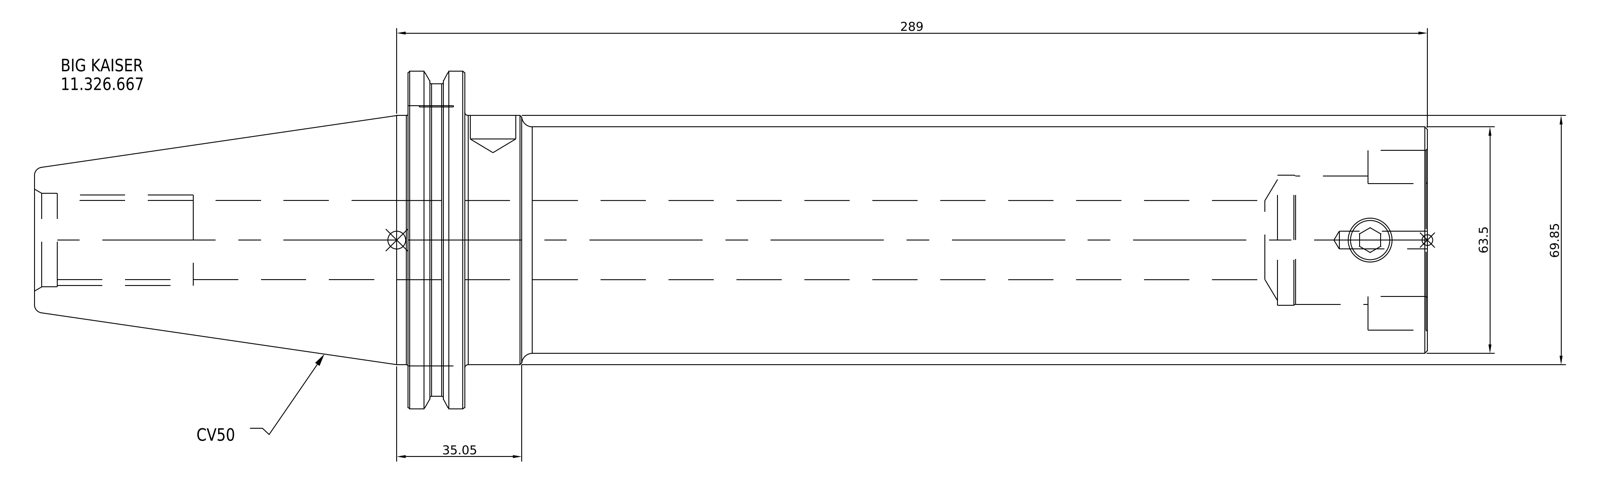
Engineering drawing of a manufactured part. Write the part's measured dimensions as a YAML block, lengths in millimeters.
part_name: "11.326.667"
step_written_by: "SolidWorks 2021 (CONFIG_CONTROL_DESIGN)"
units: millimeters
bodies: {solids: 1, faces: 16, planar: 7, cylindrical: 6, other: 3}
overall_size: [390.6, 98.43, 98.43]
volume: 1241000
surface_area: 91460
round_bosses_or_shafts:
  - {diameter: 98.43, count: 1}
  - {diameter: 91.29, count: 1}
  - {diameter: 69.85, count: 1}
  - {diameter: 63.27, count: 1}
face_to_face_distances: [17.55, 269.95, 287.5, 390.6, 120.65, 103.1, 254, 15.95, 33.5, 136.6]
